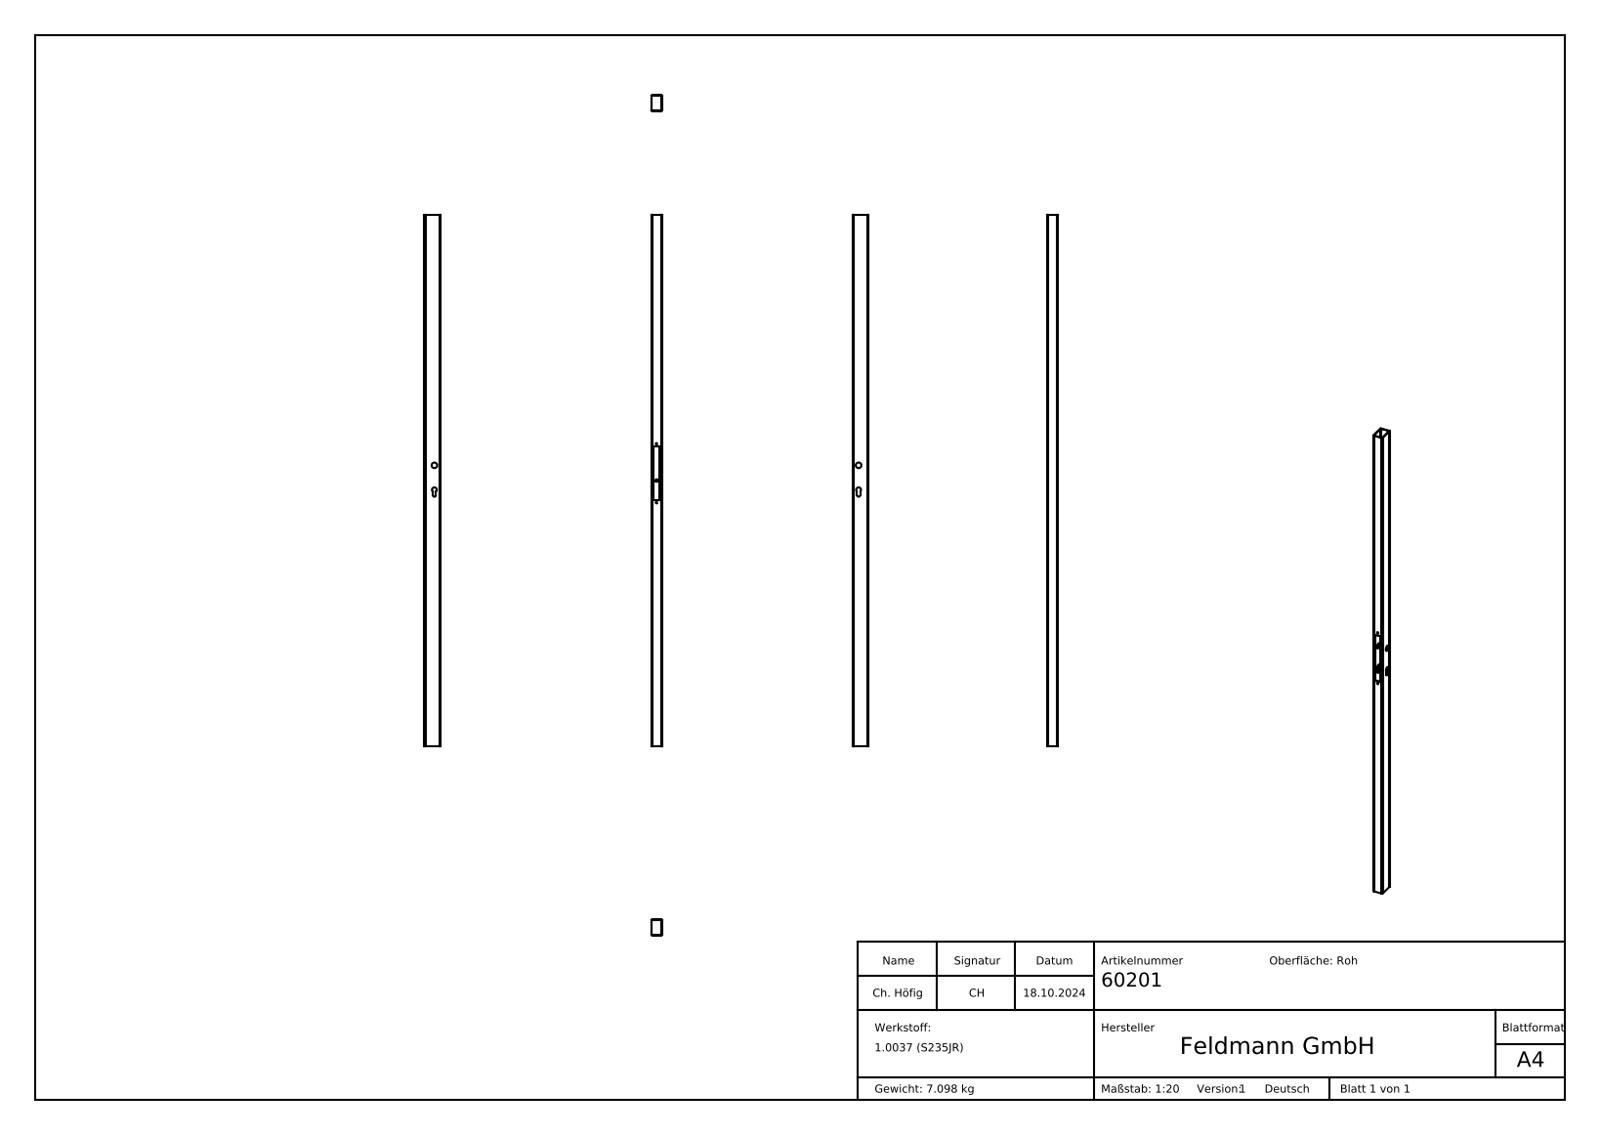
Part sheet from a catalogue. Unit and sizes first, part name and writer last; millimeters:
Units: millimetres
Overall size (bounding box): 1995 × 60 × 40
Round holes (diameter × count): ⌀4.2 ×2, ⌀21 ×1
Partial cylindrical surfaces — rounded edges, fillets, slot ends (radius × count): R1.5 ×4, R4 ×4, R5.65 ×1, R9.15 ×1
Main face-to-face distances: 2.5, 37.5, 57.5, 40, 35, 60, 55, 10, 30, 7.5
Hole centre spacings: 221
Volume: 910 051 mm³ · Surface area: 730 919 mm²
Bodies: 1 solid, 246 faces (129 planar, 16 cylindrical, 101 other)
Part name (STEP PRODUCT): 60201
STEP written by: SolidWorks 2018 (CONFIG_CONTROL_DESIGN)
